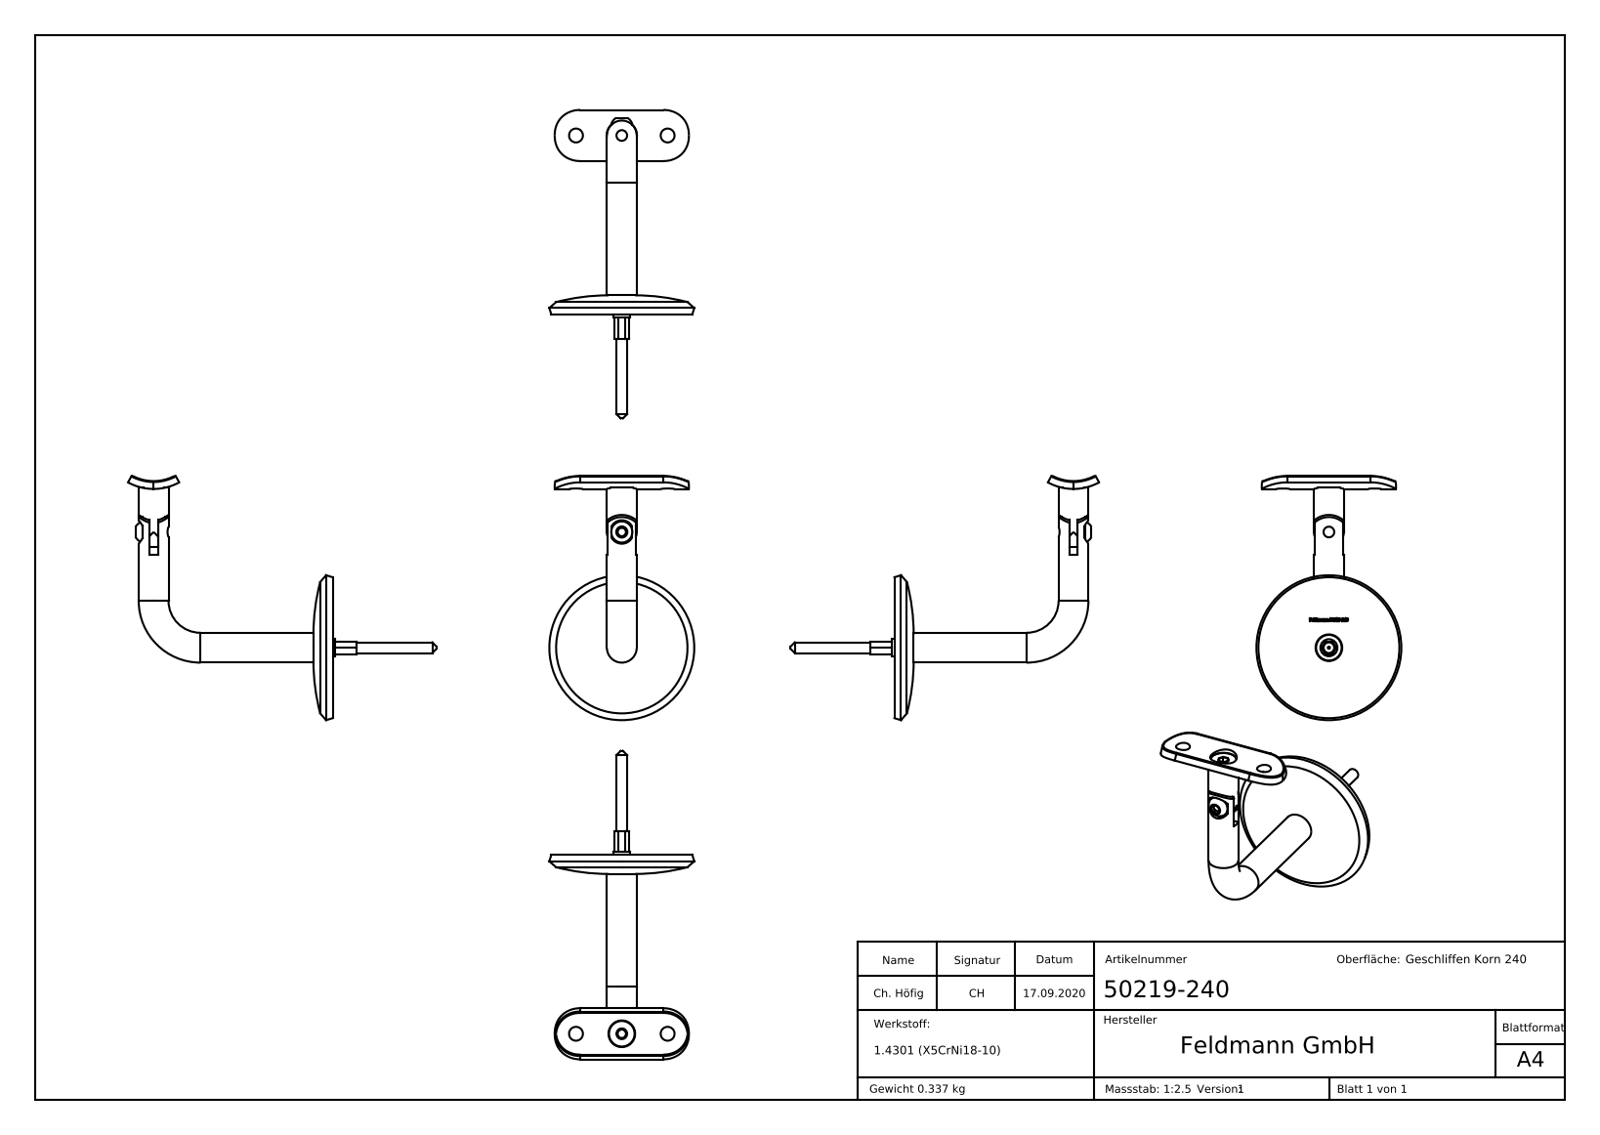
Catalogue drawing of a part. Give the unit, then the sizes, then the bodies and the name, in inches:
Units: inches
Overall size (bounding box): 5.698 × 4.513 × 2.676
Round holes (diameter × count): ⌀0.256 ×3, ⌀0.197 ×2, ⌀0.492 ×2, ⌀0.268 ×1
Round bosses / shafts (diameter × count): ⌀0.551 ×2, ⌀0.236 ×2, ⌀0.472 ×1, ⌀0.413 ×1, ⌀0.315 ×1, ⌀0.197 ×1
Partial cylindrical surfaces — rounded edges, fillets, slot ends (radius × count): R0.004 ×18, R0.472 ×4, R0.02 ×2, R0.217 ×1, R0.276 ×1, R0.28 ×1, R0.394 ×1, R0.413 ×1
Main face-to-face distances: 0.159, 0.161, 0.157, 0.118, 0.116, 0.276, 0.278, 0.087, 0.236, 1.228
Hole centre spacings: 0.846, 1.693, 2.138
Volume: 2.685 in³ · Surface area: 35.97 in²
Bodies: 7 solids, 463 faces (55 planar, 221 cylindrical, 187 other)
Part name (STEP PRODUCT): 50219-240 Teil5; 50219-240; 50219-240 Teil5_50219-240 Teil 4 Keyshot; 50219-240 Teil2 (+8 more)
STEP written by: SolidWorks 2018 (CONFIG_CONTROL_DESIGN)
